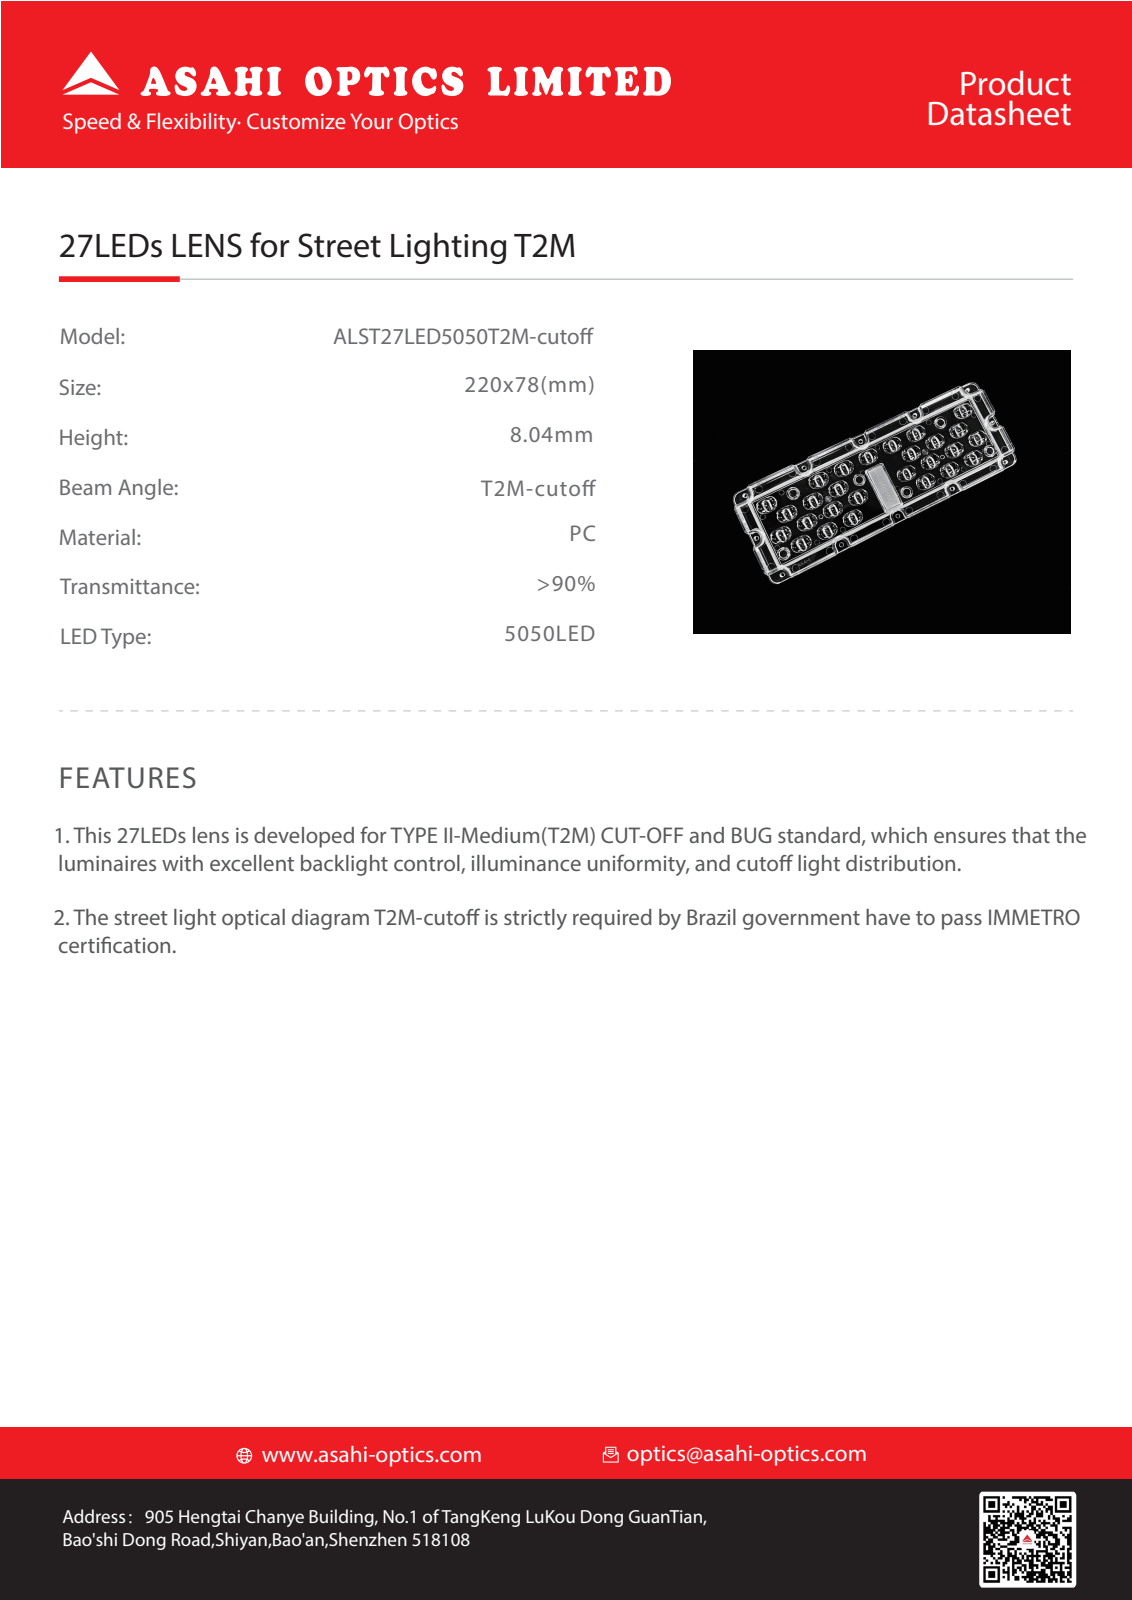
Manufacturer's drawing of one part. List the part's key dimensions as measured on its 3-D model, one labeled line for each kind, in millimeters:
Part name (STEP PRODUCT): M27
STEP written by: PRO/ENGINEER BY PARAMETRIC TECHNOLOGY CORPORATION, 2015070 (CONFIG_CONTROL_DESIGN)
Units: millimetres
Bodies: 1 solid, 994 faces (326 planar, 170 cylindrical, 498 other)
Overall size (bounding box): 219.96 × 77.96 × 8.2
Round holes (diameter × count): ⌀3.5 ×12
Partial cylindrical surfaces — rounded edges, fillets, slot ends (radius × count): R0.4 ×36, R1.5 ×30, R0.8 ×24, R1.7 ×4, R2 ×4, R2.5 ×4, R3 ×4
Main face-to-face distances: 2.36, 1.5, 3.86, 6.2, 2, 2.15, 0.65, 1.71, 4.7, 4.05
Hole centre spacings: 50, 84.4, 100, 120.93, 68, 34.53, 65.51, 111.32
